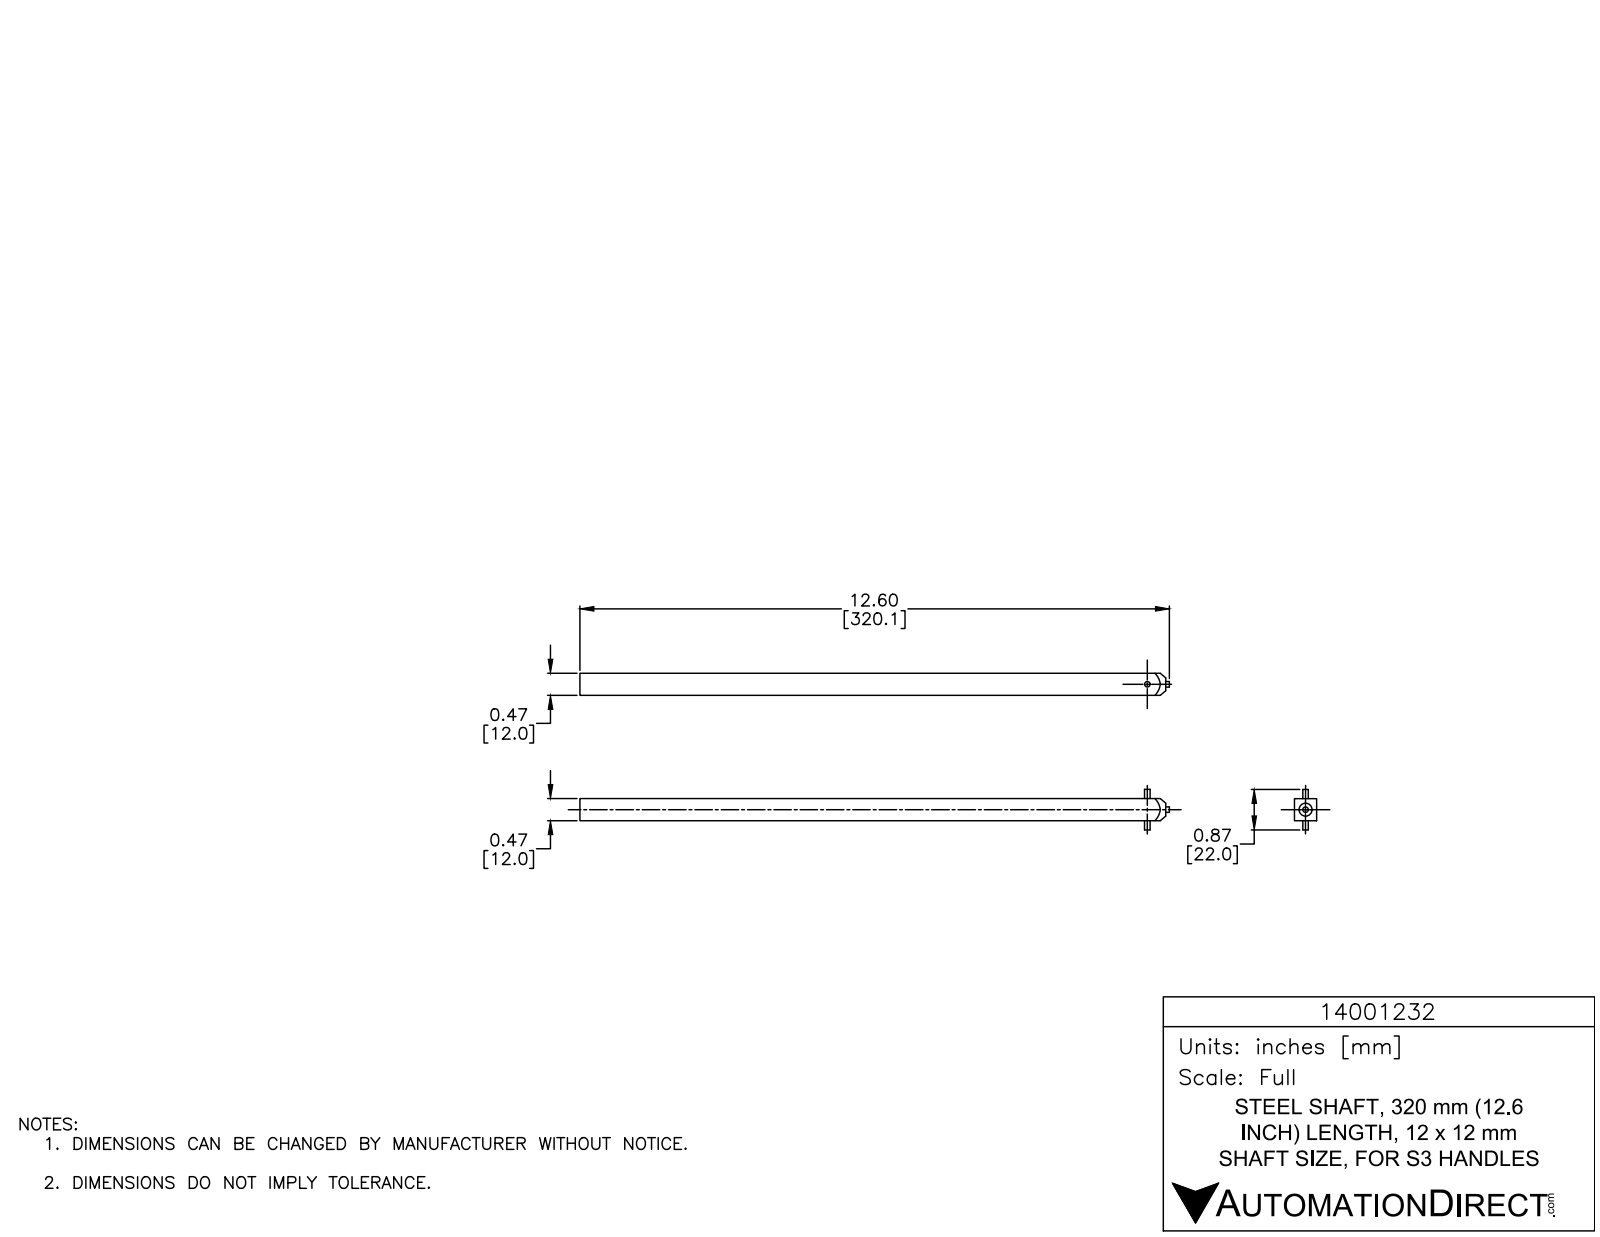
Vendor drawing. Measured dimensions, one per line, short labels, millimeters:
name: 14001232
written by: SolidWorks 2015 (AUTOMOTIVE_DESIGN)
unit: mm
bodies: 2 solids, 19 faces (13 planar, 6 cylindrical, 0 other)
size: 320 × 22 × 12
volume: 45 691 mm³; area: 15 795 mm²
holes: 1× ⌀3.1
bosses: 2× ⌀3
face distances: 12, 318, 5, 17, 320, 2, 22
